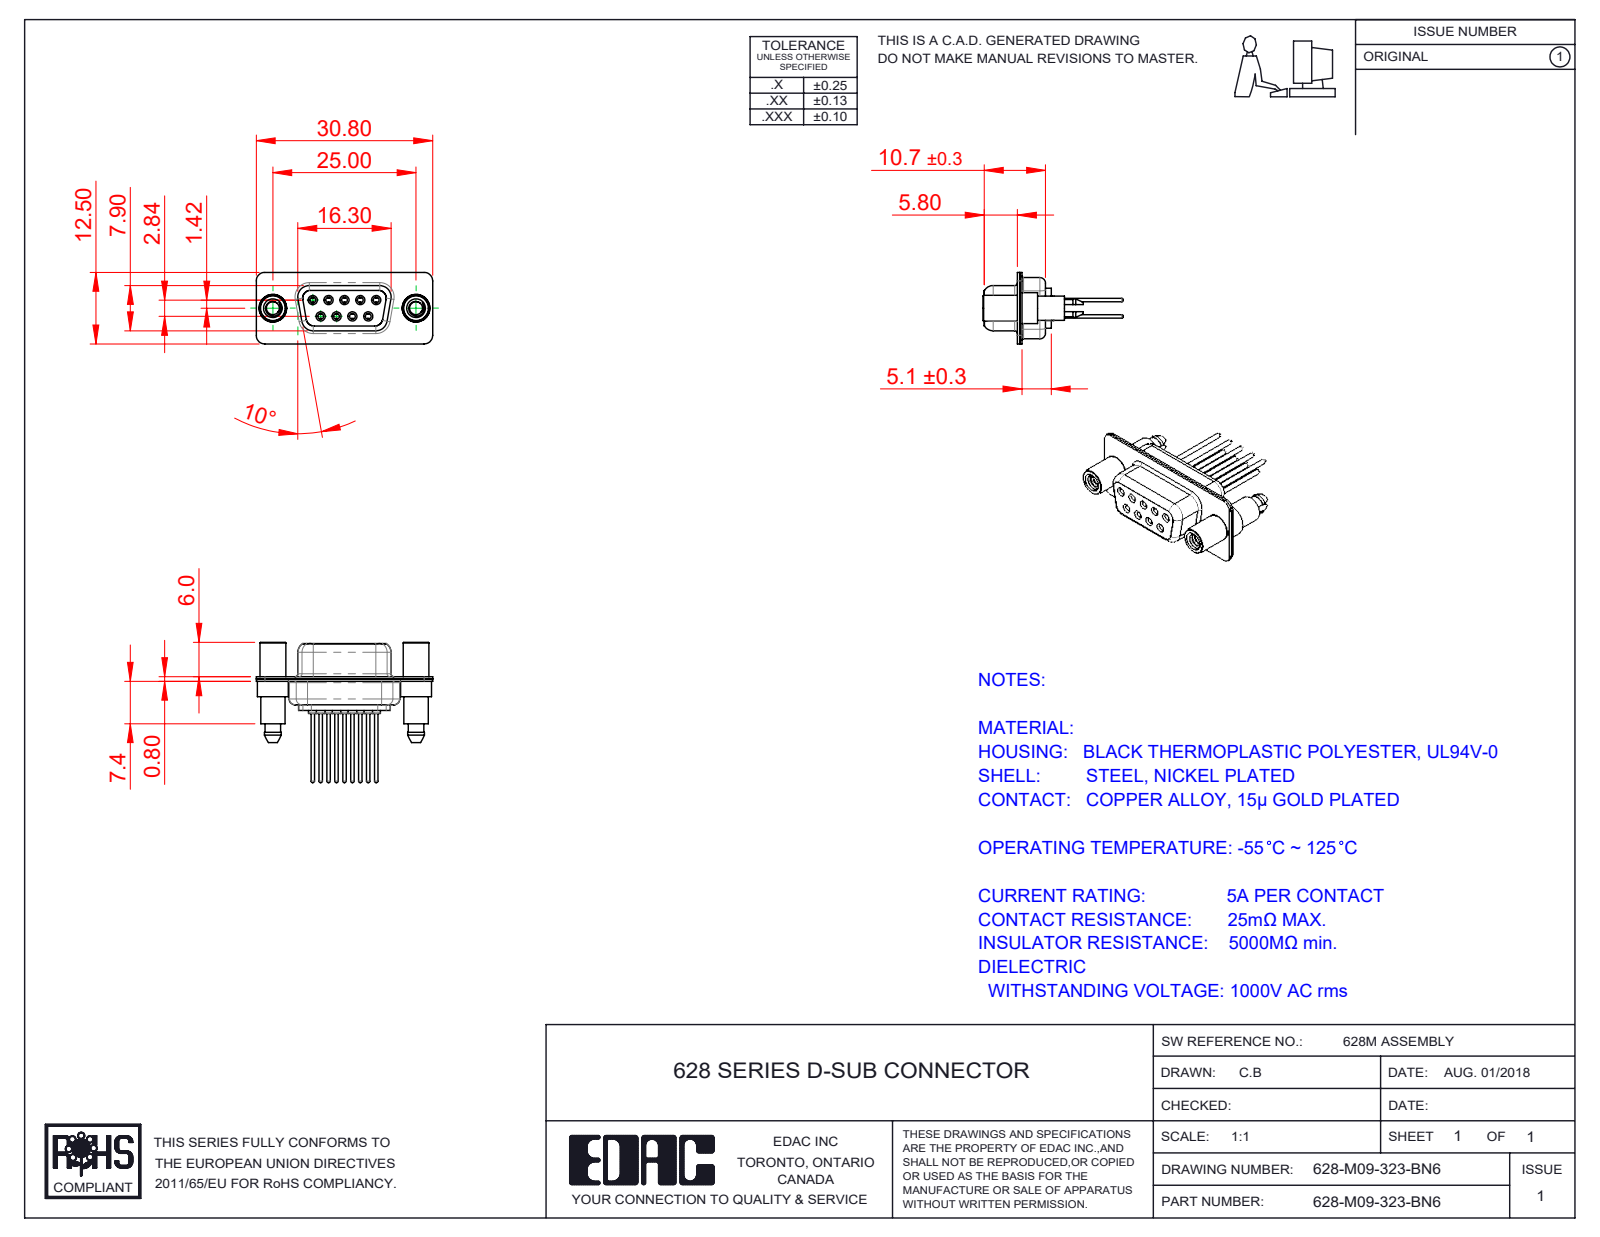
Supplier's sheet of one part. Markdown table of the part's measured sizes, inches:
| quantity | value |
| --- | --- |
| part name | 628M Shell Rear_09 Contacts; 628M Contact Row 1_23; 628-M09-323-BN6; 628M 4-40 Threaded Standoff and Boardlock (+3 more) |
| STEP written by | SolidWorks 2020 (CONFIG_CONTROL_DESIGN) |
| units | inches |
| bodies | 14 solids, 826 faces (220 planar, 336 cylindrical, 270 other) |
| overall size | 1.213 × 0.963 × 0.492 |
| volume | 0.126 in³ |
| surface area | 7.756 in² |
| round holes (diameter × count) | 0.039 × 9, 0.043 × 9, 0.067 × 9, 0.071 × 9, 0.079 × 9, 0.089 × 2, 0.157 × 2, 0.189 × 2 |
| round bosses / shafts (diameter × count) | 0.087 × 9, 0.063 × 9, 0.059 × 9, 0.024 × 9, 0.213 × 2, 0.193 × 2, 0.177 × 2, 0.167 × 2 |
| partial cylindrical surfaces (radius × count) | 0.059 × 18, 0.079 × 12, 0.063 × 10, 0.053 × 8, 0.01 × 4, 0.02 × 4, 0.024 × 4, 0.026 × 4 |
| main face-to-face distances | 0.016, 0.055, 0.018, 0.333, 0.031, 0.071, 0.039, 0.35, 0.244, 0.366 |
| hole center spacings | 0.124, 0.109, 0.218, 0.198, 0.198, 0.327, 0.28, 0.294 |
